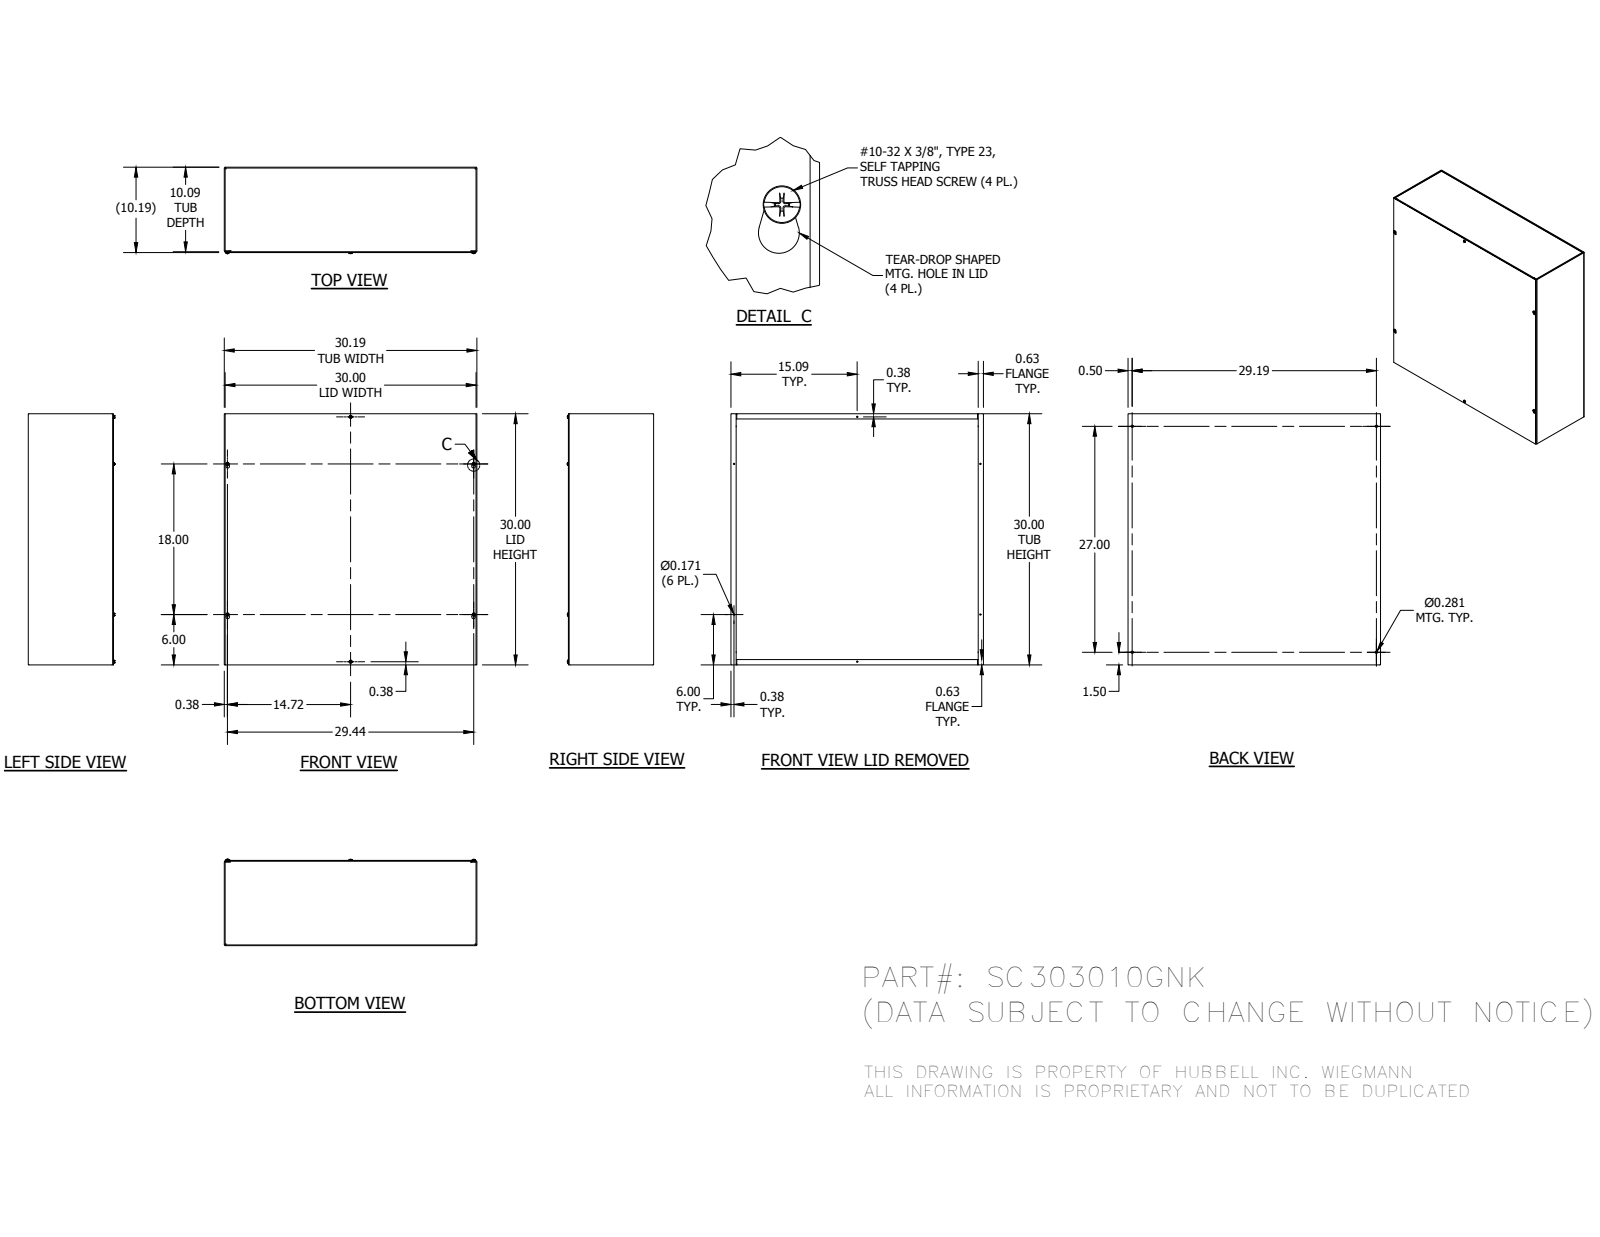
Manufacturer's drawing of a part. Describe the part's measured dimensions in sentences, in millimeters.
The part is named "SC303010GNKBLR; SC3010GNKTB; SC3030GLPA; 37214 (+1 more)". Its 3-D file was written by "Autodesk Inventor 2014 (AUTOMOTIVE_DESIGN)". It is 10 solids with 404 faces: 232 planar, 50 cylindrical and 122 other. Overall it measures 766.76 by 762 by 262.11 millimeters. Its volume is 4 782 000 cubic millimeters and its surface area 4 045 000 square millimeters. Round holes: 6 of diameter 4.34, 4 of diameter 7.14, 2 of diameter 7.92. Round bosses or shafts: 6 of diameter 4.83. Partial cylindrical surfaces (rounded edges, fillets, slot ends): 12 of radius 0.4, 12 of radius 2.78, 4 of radius 3.17, 4 of radius 5.16. The main face-to-face distances are 2.38, 256.38, 254, 258.76, 762, 759.62, 764.38, 757.24, 766.76, 4.76. The hole center spacings are 371.78, 400.23, 804.82, 114.34, 571.51, 707, 753.26, 938.59.
